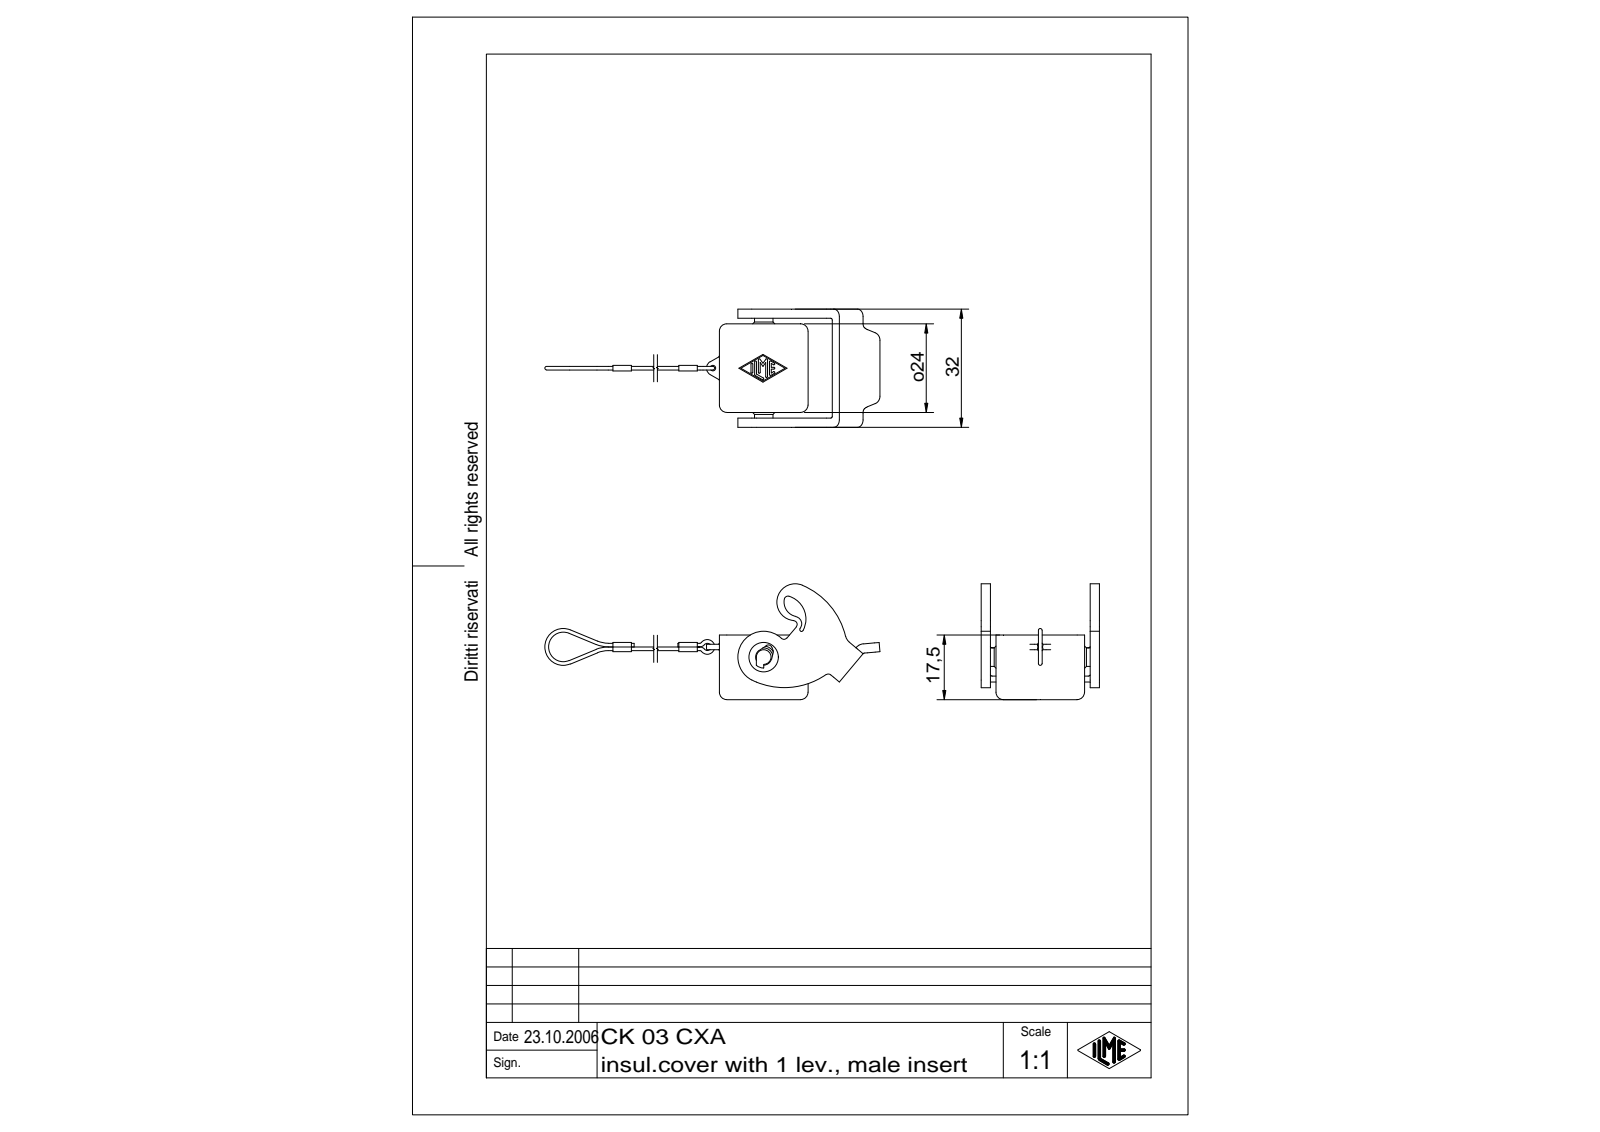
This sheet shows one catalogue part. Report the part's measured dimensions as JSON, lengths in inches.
{"part_name": "CK 03 CXA", "step_written_by": "Autodesk Inventor 7 (AUTOMOTIVE_DESIGN)", "units": "inches", "bodies": {"solids": 2, "faces": 343, "planar": 84, "cylindrical": 162, "other": 97}, "overall_size": [4.562, 1.26, 1.234], "volume_in3": 0.4, "surface_area_in2": 12.66, "round_holes": [[0.059, 1], [0.315, 1]], "round_bosses_or_shafts": [[0.039, 4], [0.197, 1], [0.157, 1]], "partial_cylinders_radius": [[0.079, 16], [0.01, 14], [0.008, 12], [0.02, 12], [0.039, 6], [0.004, 3], [0.03, 2], [0.118, 2]], "face_to_face_distances": [0.059, 0.886, 0.945, 0.098, 0.827, 0.118, 0.217, 1.043, 0.157, 1.004]}
